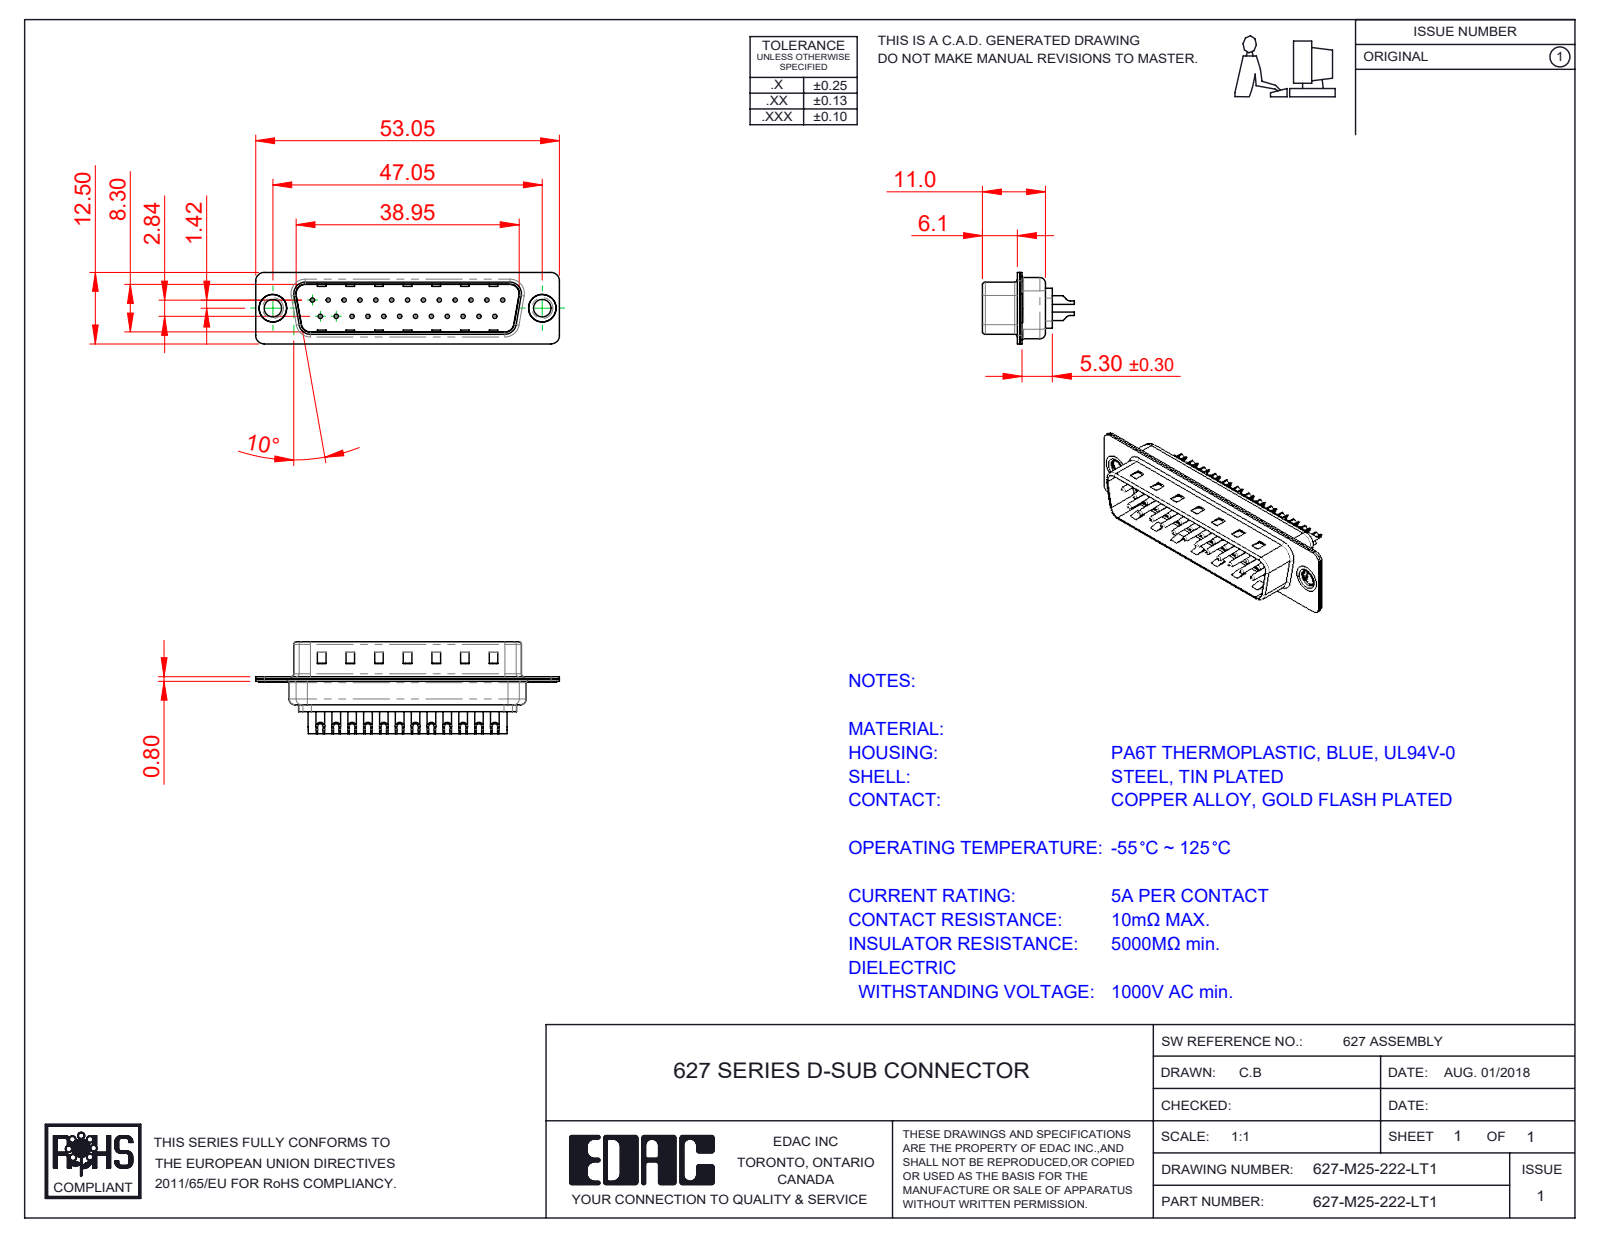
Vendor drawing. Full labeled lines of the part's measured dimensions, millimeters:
Part name (STEP PRODUCT): 627M Shell Rear_25 Contacts; 627M Thru Hole Rivet; 627M Contact Row 2_22; 627-M25-222-LT1 (+3 more)
STEP written by: SolidWorks 2020 (CONFIG_CONTROL_DESIGN)
Units: millimetres
Bodies: 30 solids, 1275 faces (396 planar, 521 cylindrical, 358 other)
Overall size (bounding box): 53.05 × 16.05 × 12.5
Volume: 2 698 mm³ · Surface area: 6 932 mm²
Round holes (diameter × count): ⌀0.75 ×25, ⌀1 ×25, ⌀1.6 ×25, ⌀2 ×25, ⌀3.05 ×2, ⌀4 ×2, ⌀4.8 ×2
Round bosses / shafts (diameter × count): ⌀1.5 ×25, ⌀5 ×2, ⌀4.9 ×2, ⌀3.55 ×2
Partial cylindrical surfaces — rounded edges, fillets, slot ends (radius × count): R1.5 ×16, R2 ×12, R0.5 ×8, R1.6 ×8, R1 ×6, R0.25 ×4, R0.6 ×4, R0.65 ×4
Main face-to-face distances: 0.4, 0.8, 9.5, 9.1, 8.7, 9.9, 1.2, 0.75, 0.35, 6.1
Hole centre spacings: 3.16, 2.77, 5.54, 8.31, 11.08, 13.85, 16.62, 5.03
